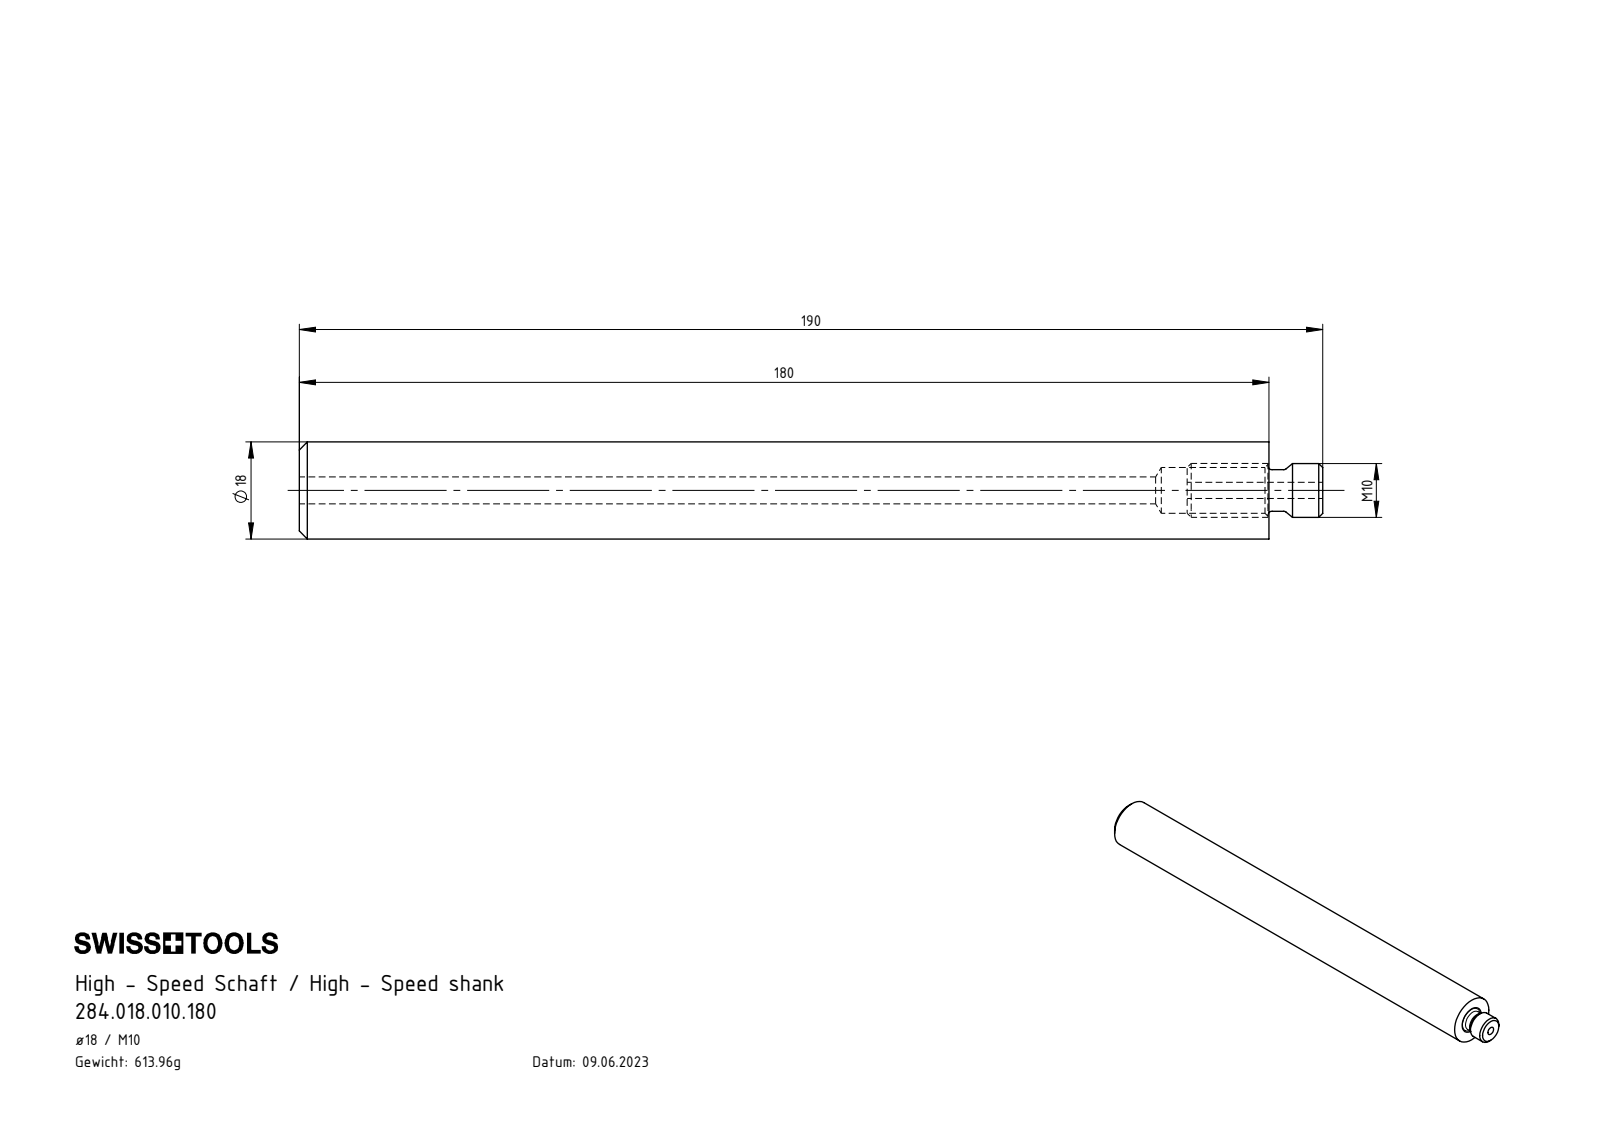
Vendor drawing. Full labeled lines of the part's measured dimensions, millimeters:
Part name (STEP PRODUCT): HM1-BG1.010.025_A; 284.018.010.180; HM1-U18.001.180_A
STEP written by: SolidWorks 2022 (AUTOMOTIVE_DESIGN)
Units: millimetres
Bodies: 2 solids, 35 faces (5 planar, 14 cylindrical, 16 other)
Overall size (bounding box): 190 × 18 × 18
Volume: 43 105 mm³ · Surface area: 14 772 mm²
Round holes (diameter × count): ⌀3 ×1, ⌀5 ×1, ⌀8.5 ×1
Round bosses / shafts (diameter × count): ⌀18 ×1, ⌀10 ×1, ⌀7.7 ×1
Main face-to-face distances: 180, 190, 10, 164.8, 15.2, 25.2, 179.8, 15, 10.2
